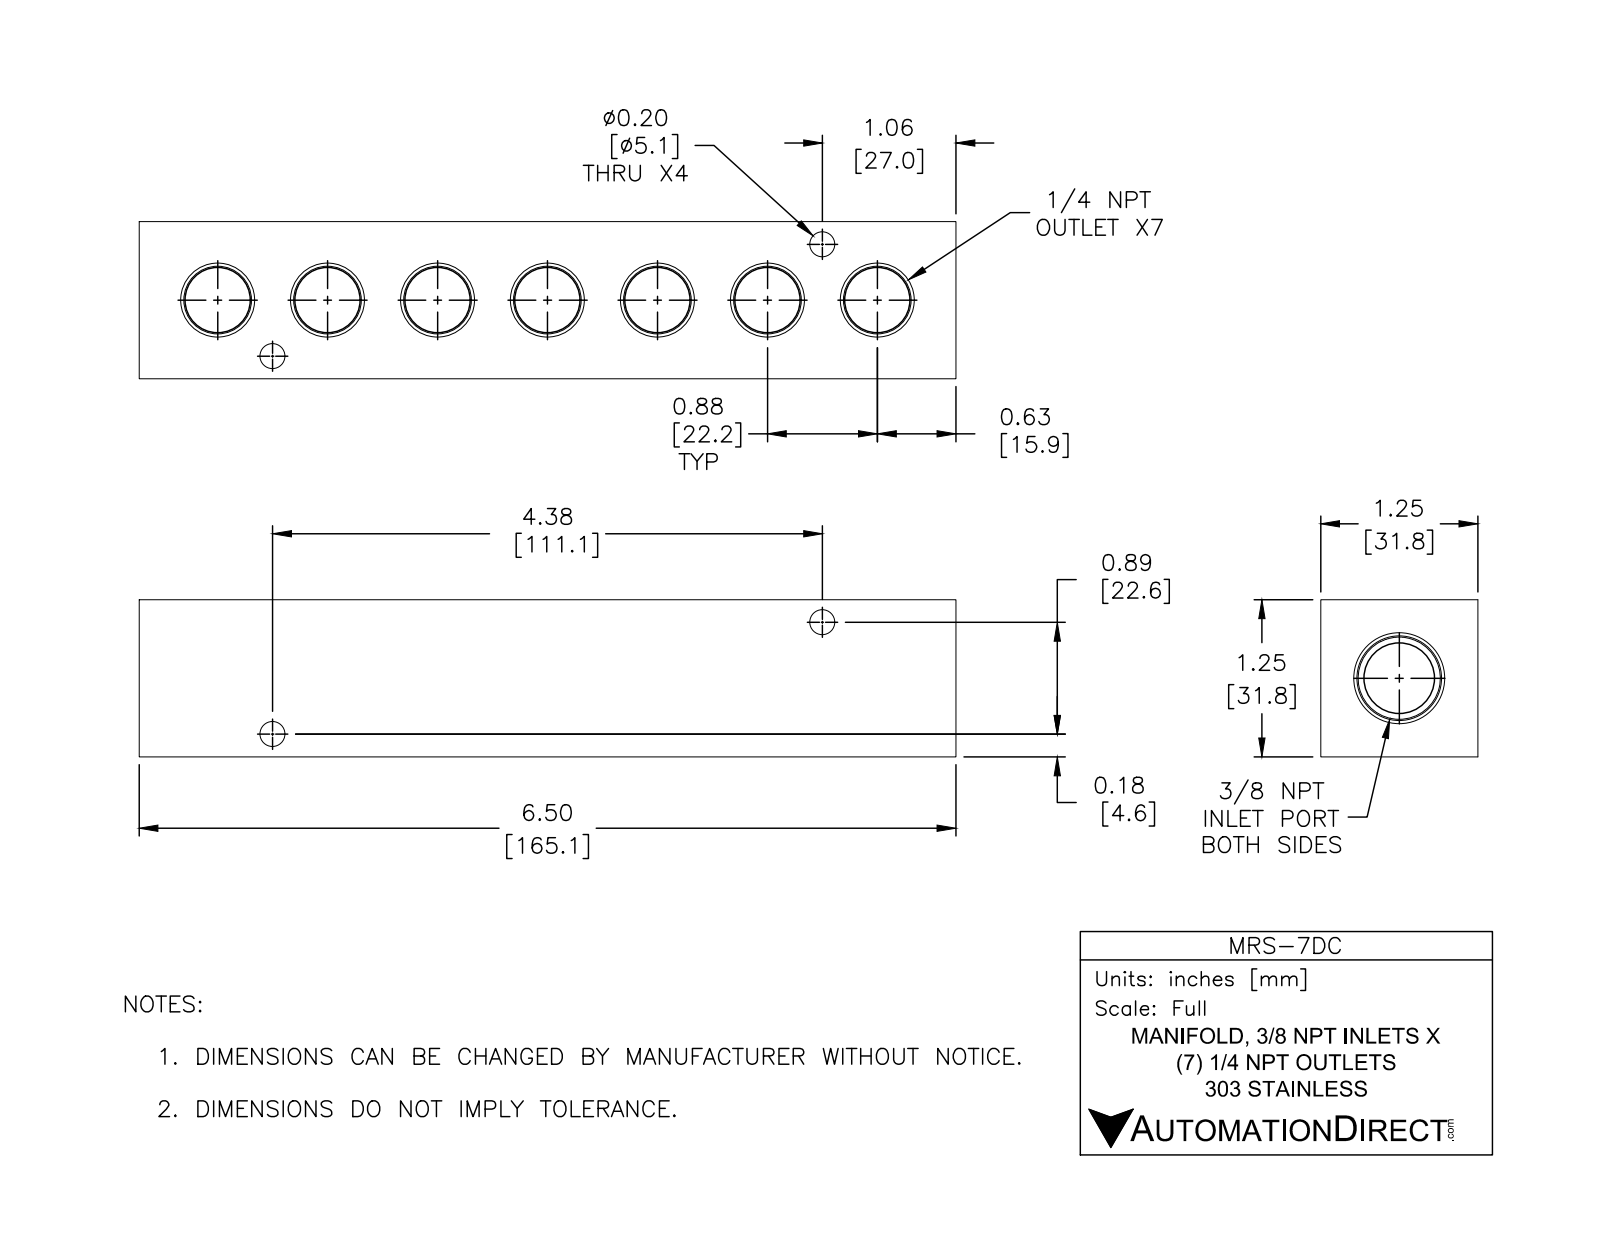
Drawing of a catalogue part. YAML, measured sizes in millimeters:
part_name: "MRS-7DC"
step_written_by: "SolidWorks 2015 (CONFIG_CONTROL_DESIGN)"
units: millimeters
bodies: {solids: 1, faces: 90, planar: 22, cylindrical: 32, other: 36}
overall_size: [165.1, 31.8, 31.8]
volume: 126900
surface_area: 32870
round_holes:
  - {diameter: 5.1, count: 4}
  - {diameter: 14.3, count: 1}
partial_cylinders:
  - {radius: 5.6, count: 7}
face_to_face_distances: [31.8, 165.1, 21.8, 9.9, 10.4, 154.7, 144.3]
hole_center_spacings: [113.4]
